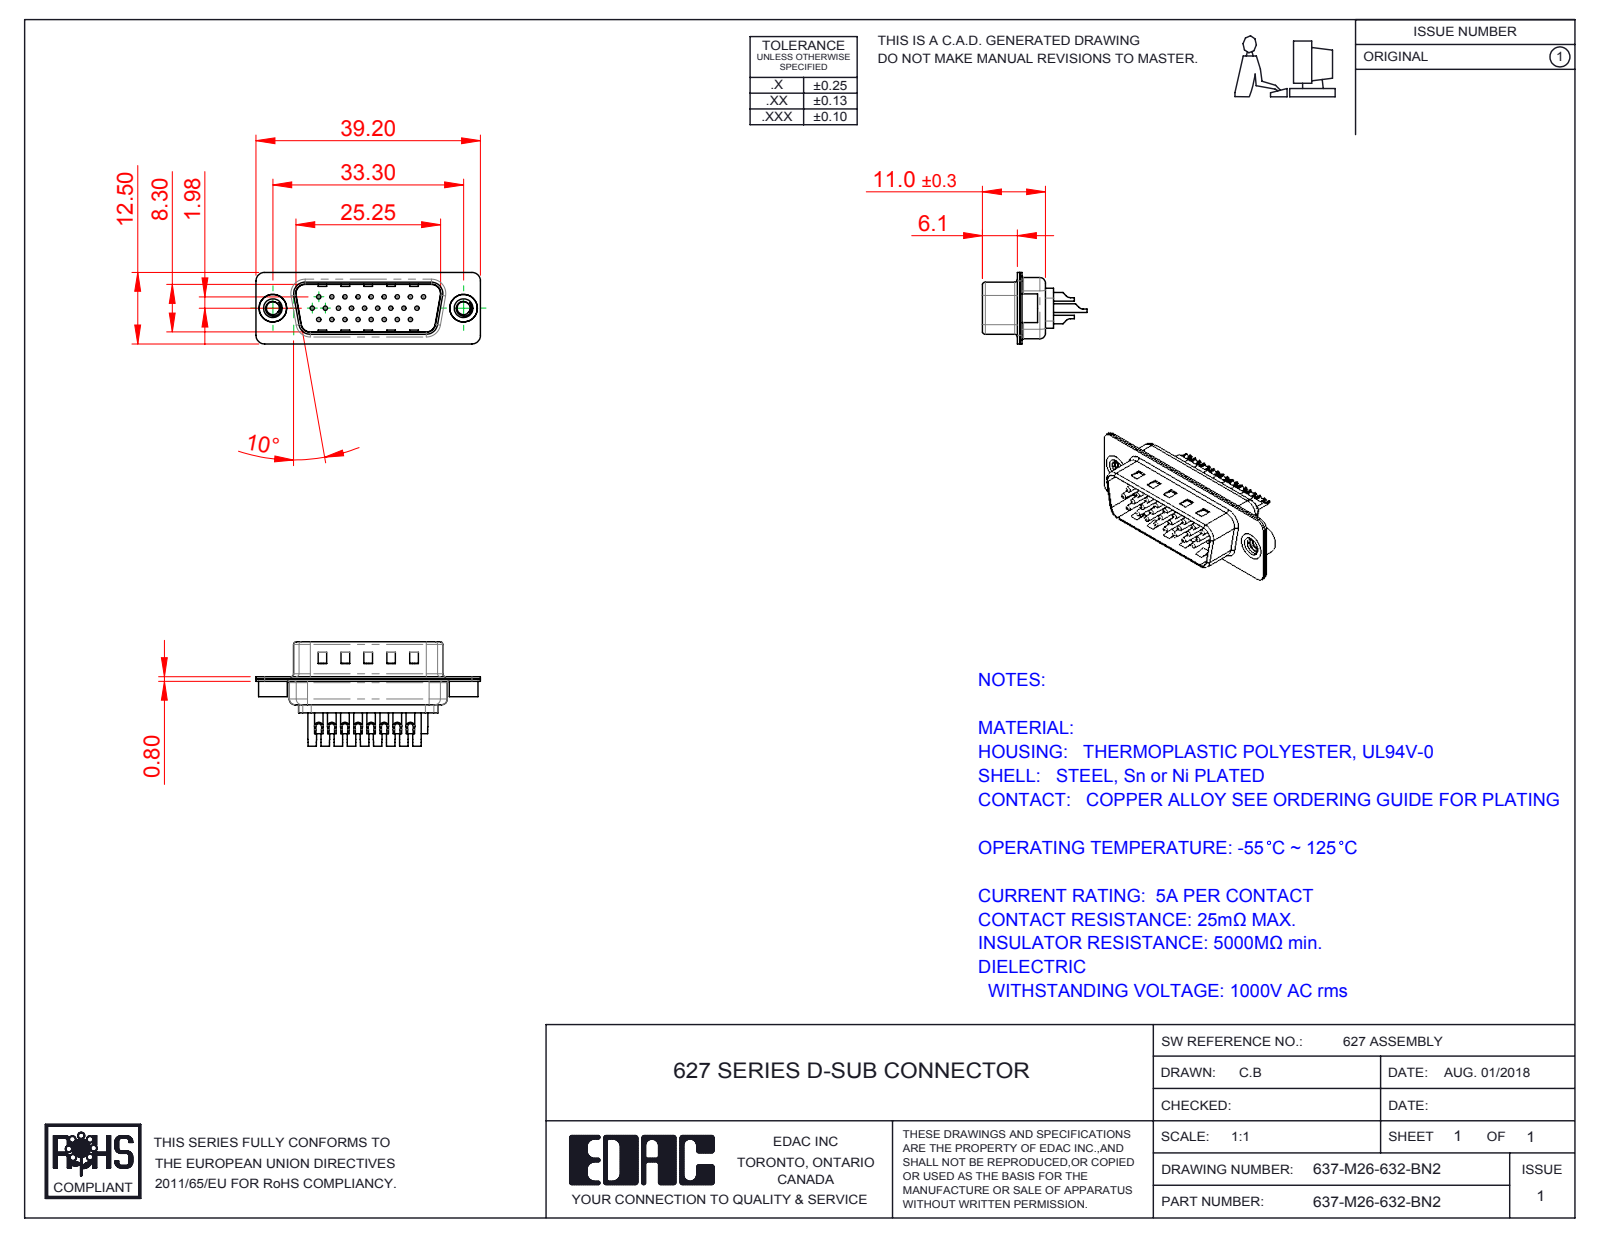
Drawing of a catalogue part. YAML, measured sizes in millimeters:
part_name: "637M Contact Row 3_32; 637M Housing_26 Contacts; 637-M26-632-BN2; 637M 4-40 Threaded Rivet (+4 more)"
step_written_by: "SolidWorks 2016 (CONFIG_CONTROL_DESIGN)"
units: millimeters
bodies: {solids: 31, faces: 1302, planar: 373, cylindrical: 549, other: 380}
overall_size: [39.2, 18.25, 12.5]
volume: 1996
surface_area: 6073
round_holes:
  - {diameter: 0.75, count: 26}
  - {diameter: 1, count: 26}
  - {diameter: 1.6, count: 26}
  - {diameter: 2, count: 26}
  - {diameter: 2.26, count: 2}
  - {diameter: 4, count: 2}
  - {diameter: 4.8, count: 2}
round_bosses_or_shafts:
  - {diameter: 1.5, count: 26}
  - {diameter: 5, count: 2}
  - {diameter: 4.9, count: 2}
partial_cylinders:
  - {radius: 1.5, count: 16}
  - {radius: 2, count: 12}
  - {radius: 0.5, count: 8}
  - {radius: 1.6, count: 8}
  - {radius: 1, count: 7}
  - {radius: 0.25, count: 4}
  - {radius: 0.6, count: 4}
  - {radius: 0.65, count: 4}
face_to_face_distances: [0.4, 0.8, 9.5, 9.1, 8.7, 9.9, 0.75, 0.35, 1.2, 1.1]
hole_center_spacings: [3.96, 2.28, 4.57, 6.05, 2.29, 8.24, 6.86, 10.48]
